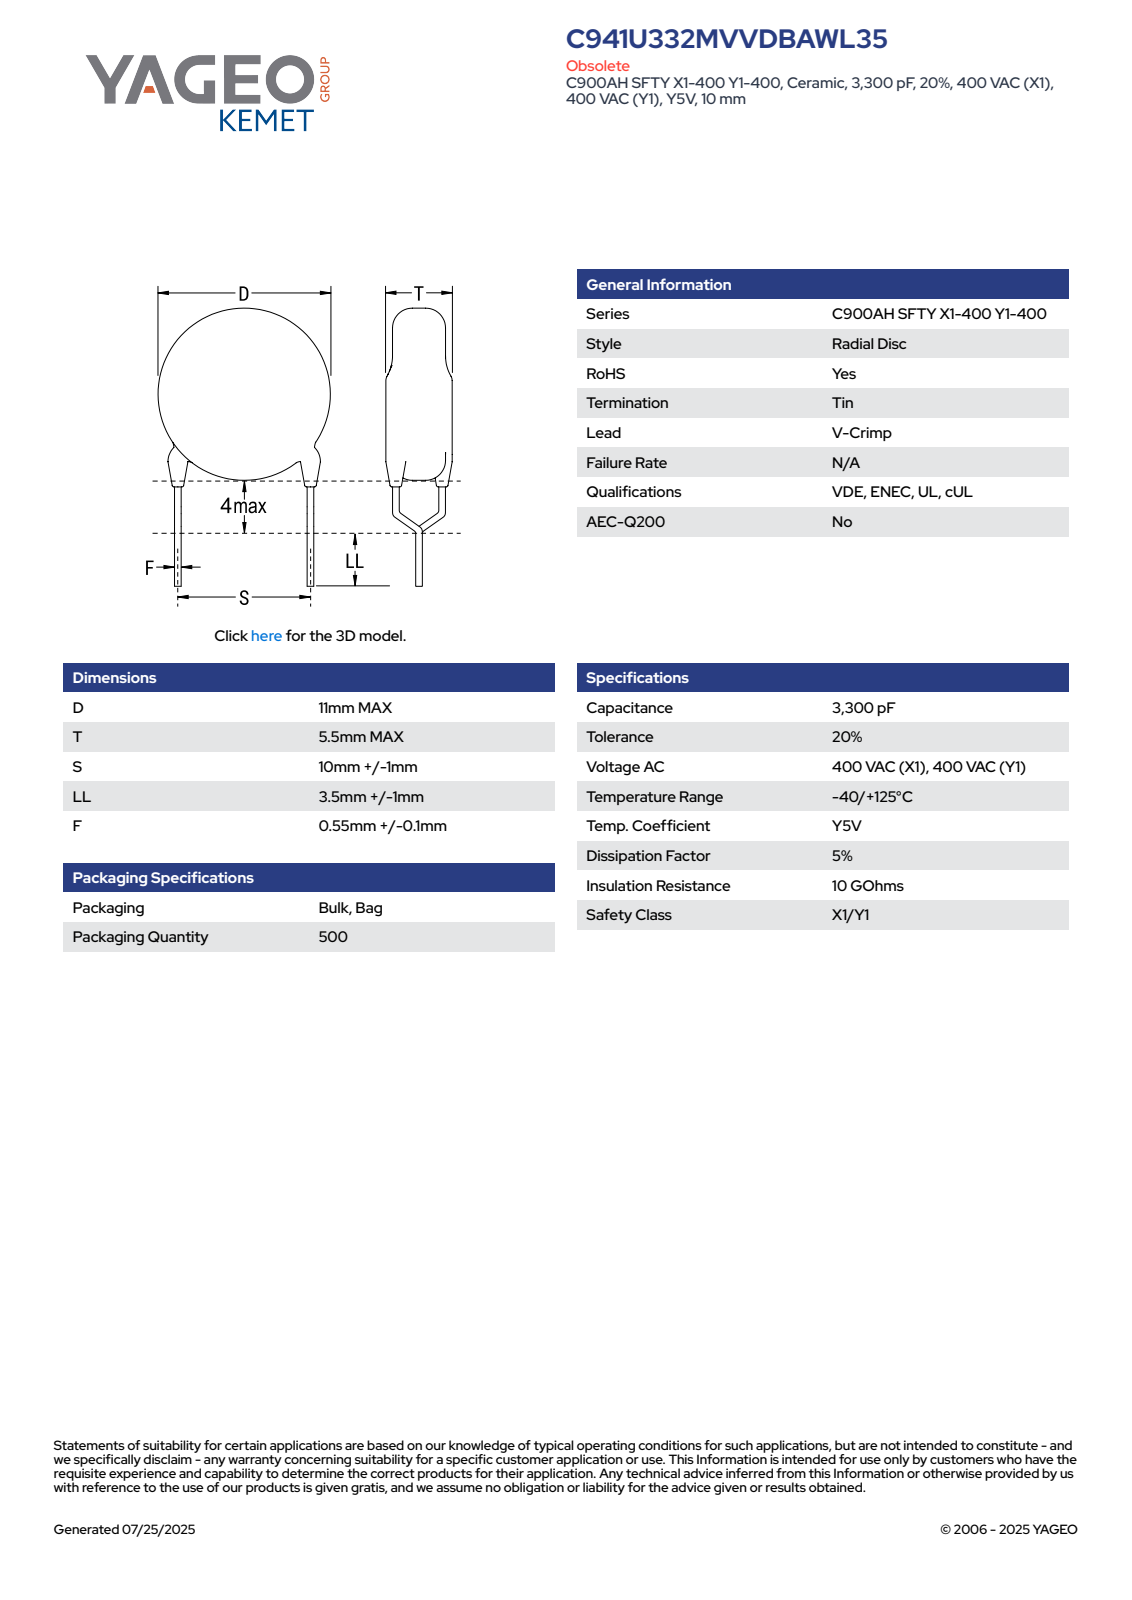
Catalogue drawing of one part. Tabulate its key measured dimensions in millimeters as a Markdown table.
| quantity | value |
| --- | --- |
| part name | CCD_VCC900_D11T5.5S10LL4.5F0.65 |
| STEP written by | SolidWorks 2014 (AUTOMOTIVE_DESIGN) |
| units | millimeters |
| bodies | 5 solids, 93 faces (65 planar, 16 cylindrical, 12 other) |
| overall size | 19.3 × 11 × 5.5 |
| volume | 518 mm³ |
| surface area | 410 mm² |
| round bosses / shafts (diameter × count) | 0.65 × 6, 11 × 1 |
| main face-to-face distances | 5.5, 7.4, 14.51, 7.11, 13.08, 5.68, 1.43, 0.39, 0.35, 5.84 |
